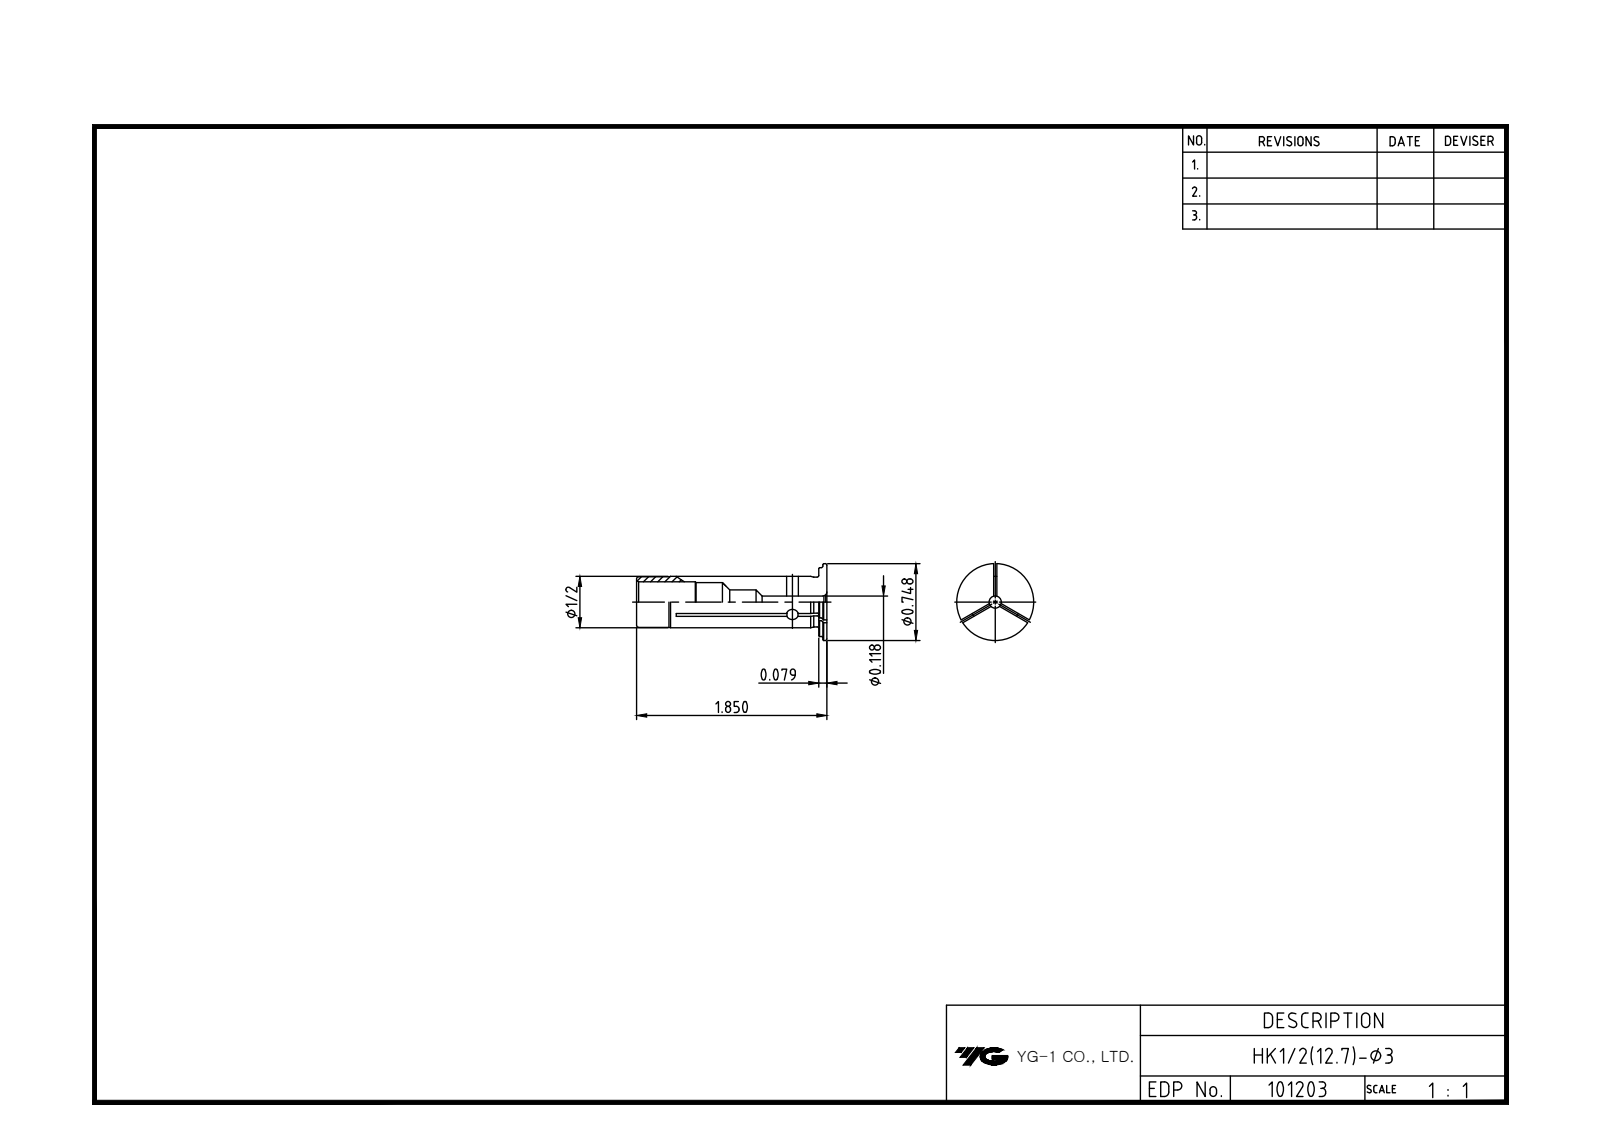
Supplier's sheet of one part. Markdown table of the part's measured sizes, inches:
| quantity | value |
| --- | --- |
| part name | LO-HK12.7-3 |
| STEP written by | Autodesk Inventor 2025 (AP242_MANAGED_MODEL_BASED_3D_ENGINEERING_MIM_LF) |
| units | inches |
| bodies | 1 solid, 14 faces (4 planar, 7 cylindrical, 3 other) |
| overall size | 1.85 × 0.748 × 0.748 |
| volume | 0.255 in³ |
| surface area | 5.295 in² |
| round holes (diameter × count) | 0.118 × 1, 0.236 × 1, 0.378 × 1, 0.394 × 1 |
| round bosses / shafts (diameter × count) | 0.748 × 1, 0.669 × 1, 0.5 × 1 |
| main face-to-face distances | 0.039, 0.079, 1.772, 1.811, 1.85 |
